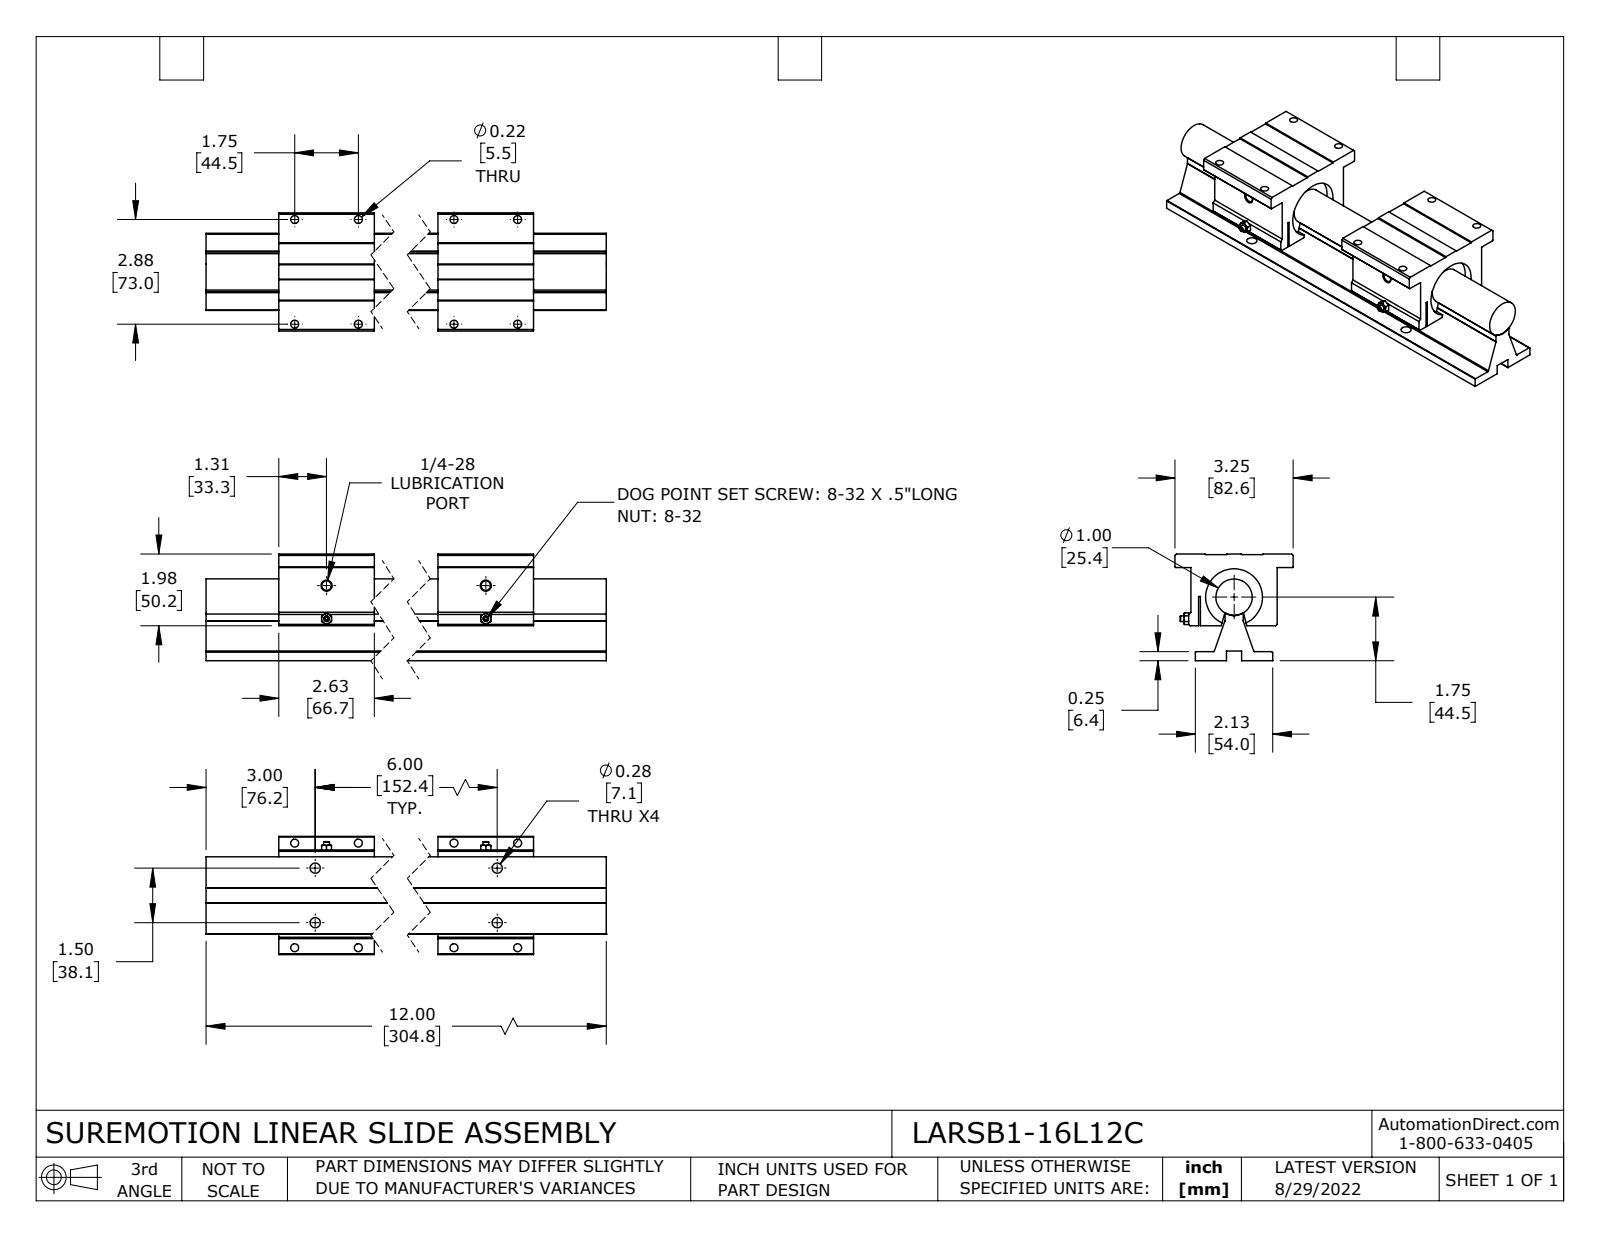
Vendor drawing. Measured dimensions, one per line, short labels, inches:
name: LARSB1-16L12C-RAIL; LARSACC-006; LARSB1-16L12C
written by: SolidWorks 2021 (CONFIG_CONTROL_DESIGN)
unit: in
bodies: 6 solids, 207 faces (121 planar, 66 cylindrical, 20 other)
size: 12 × 3.25 × 2.937
volume: 43.54 in³; area: 221.7 in²
holes: 8× ⌀0.218, 4× ⌀0.281, 2× ⌀0.258, 1× ⌀1, 1× ⌀1.562
bosses: 2× ⌀0.157
rounds: 11× R0.03, 1× R0.075, 1× R0.499
face distances: 0.25, 2.937, 2.687, 0.962, 0.712, 1.975, 5.375, 2.376, 0.981, 1.396
hole spacings: 0.888, 1.372, 1.75, 2.259, 2.489, 2.875, 3.366, 4.861
